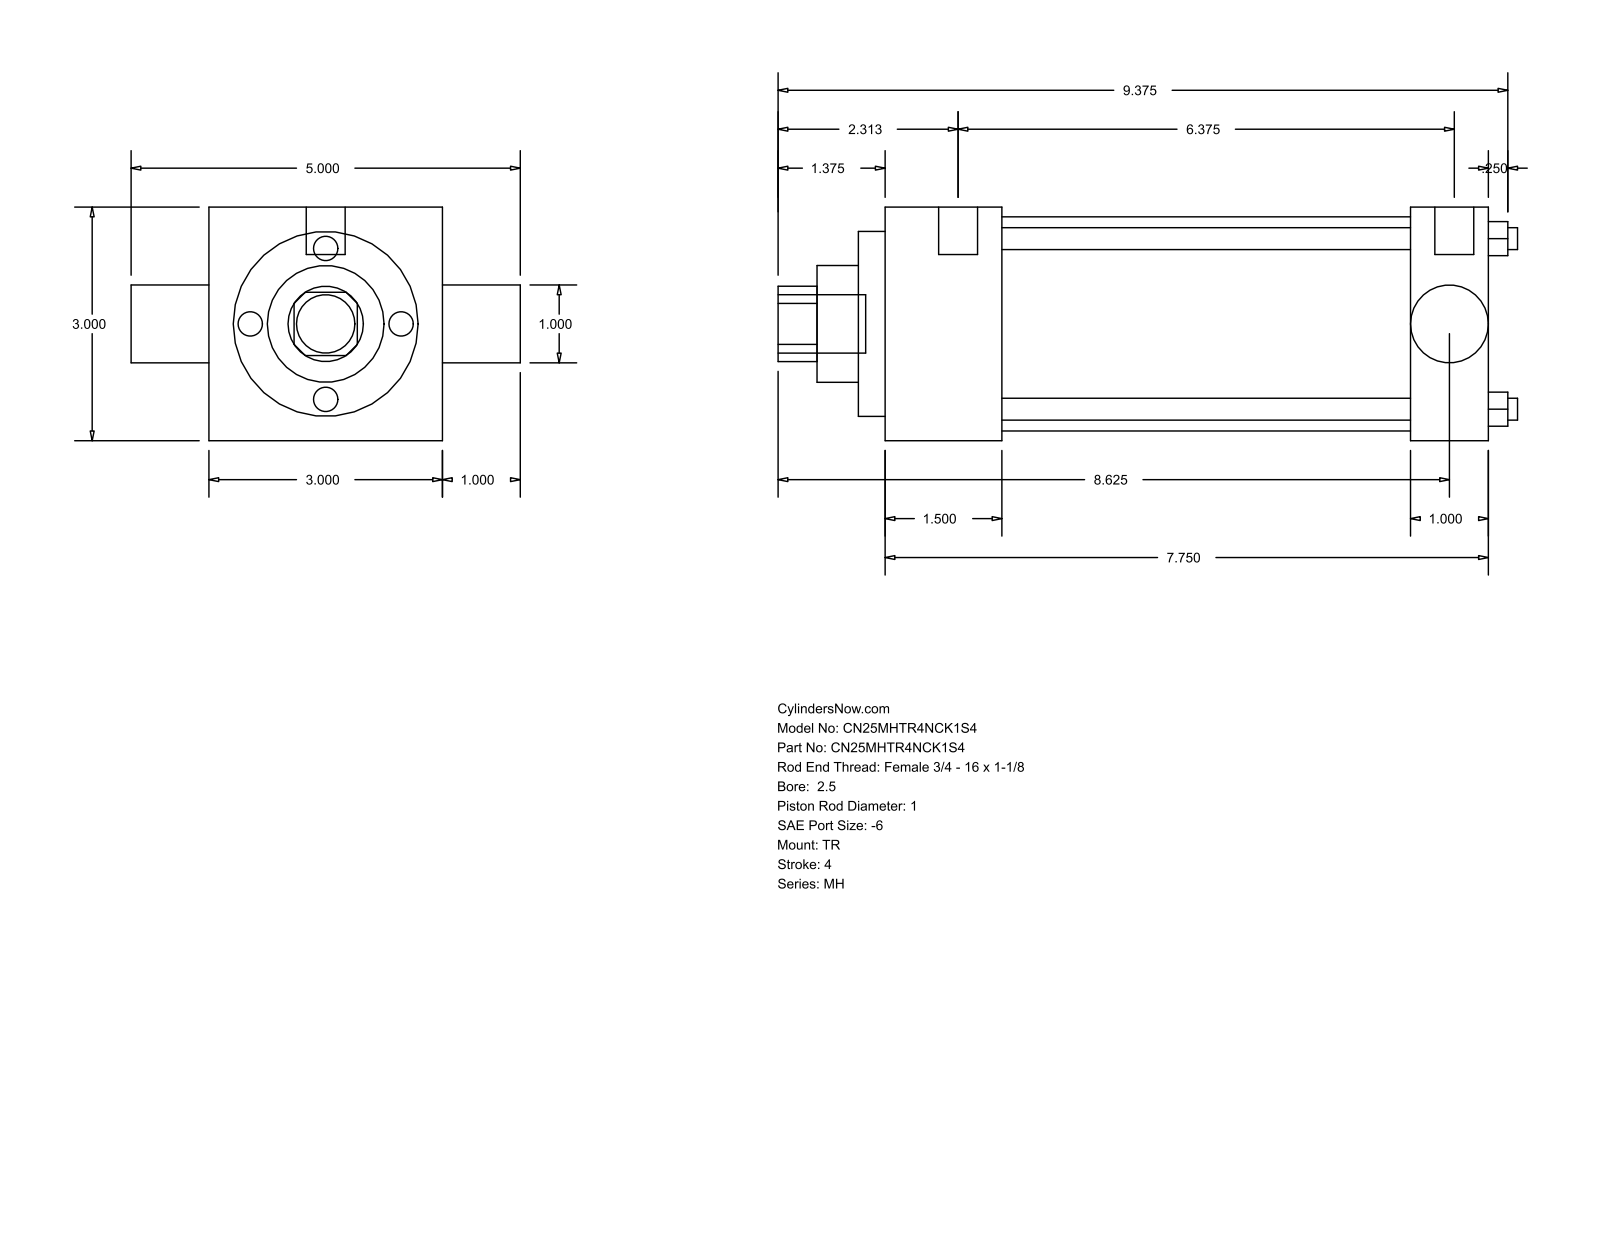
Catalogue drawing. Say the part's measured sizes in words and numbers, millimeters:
The part is named "MH_TR__0250_1". Its 3-D file was written by "GSSL Pune (CONFIG_CONTROL_DESIGN)". It is 0 solids with 86 faces: 61 planar, 25 cylindrical and 0 other. Overall it measures 241.3 by 127 by 76.2 millimeters. Round holes: 4 of diameter 7.14, 1 of diameter 25.35, 1 of diameter 25.4, 1 of diameter 38.1, 1 of diameter 60.33, 1 of diameter 69.85. Round bosses or shafts: 3 of diameter 5.56, 2 of diameter 12.7, 1 of diameter 19.05. Partial cylindrical surfaces (rounded edges, fillets, slot ends): 1 of radius 12.29. The main face-to-face distances are 76.2, 196.86, 25.4, 38.11, 158.75, 171.46, 133.35, 8.73, 46.84, 180.19. The hole center spacings are 39.33, 55.62, 78.66.
